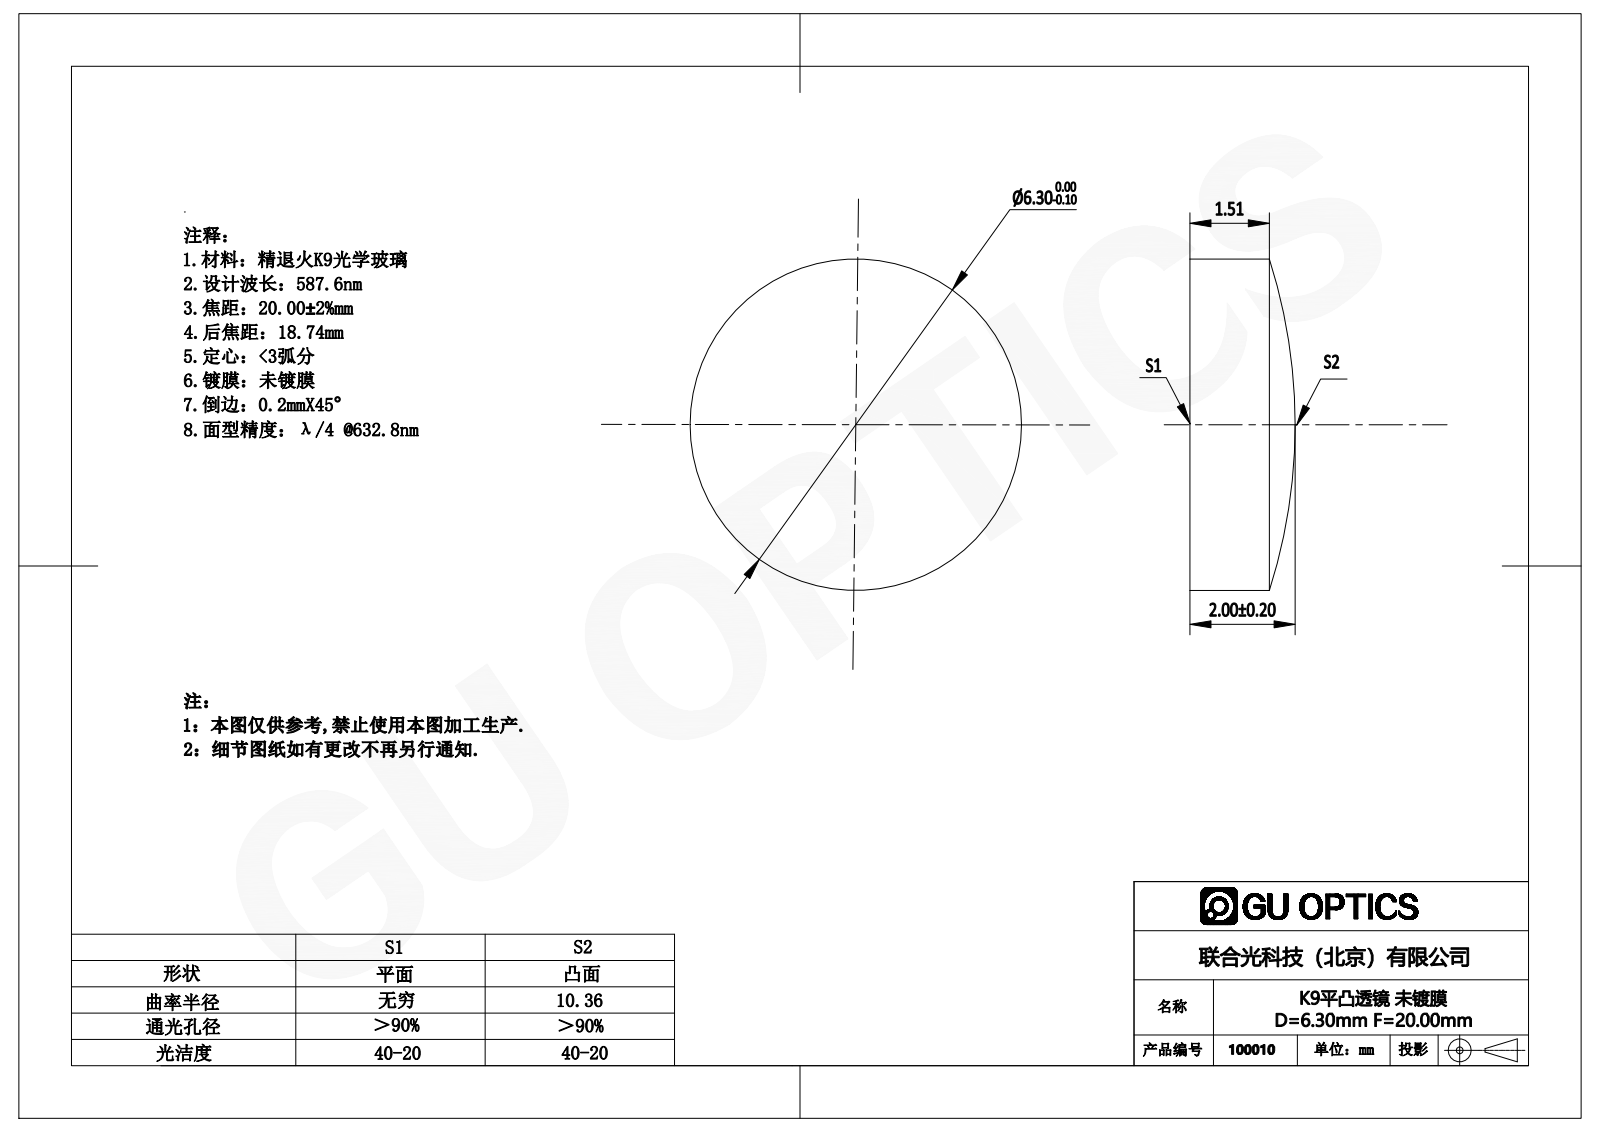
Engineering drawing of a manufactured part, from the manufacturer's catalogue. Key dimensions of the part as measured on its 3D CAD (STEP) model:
Part name (STEP PRODUCT): 100010
STEP written by: SolidWorks 2016 (AUTOMOTIVE_DESIGN)
Units: millimetres
Bodies: 1 solid, 5 faces (1 planar, 2 cylindrical, 2 other)
Overall size (bounding box): 6.3 × 6.3 × 2
Volume: 55 mm³ · Surface area: 93 mm²
Round bosses / shafts (diameter × count): ⌀6.3 ×1
